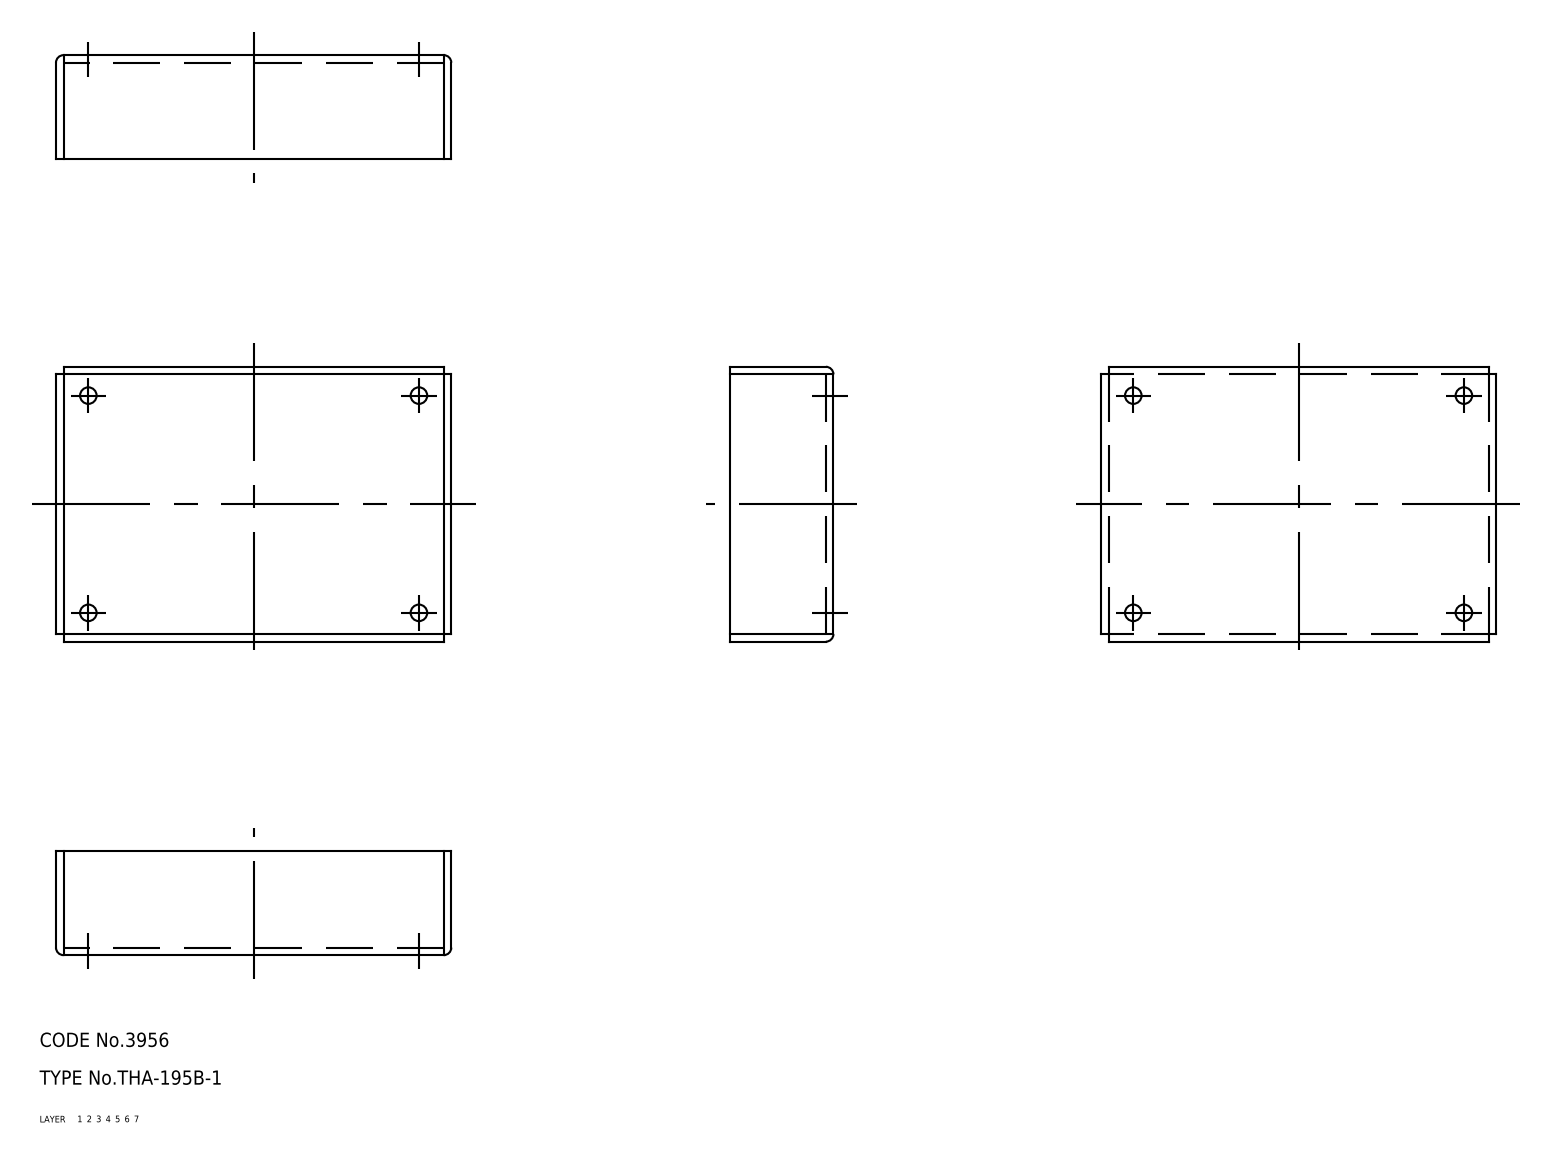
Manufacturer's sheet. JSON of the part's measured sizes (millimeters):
{"part_name": "bracket", "step_written_by": "CADfix (AUTOMOTIVE_DESIGN)", "units": "millimeters", "bodies": {"solids": 1, "faces": 34, "planar": 0, "cylindrical": 0, "other": 34}, "overall_size": [83.7, 58.2, 22], "volume_mm3": 16380, "surface_area_mm2": 21296}
